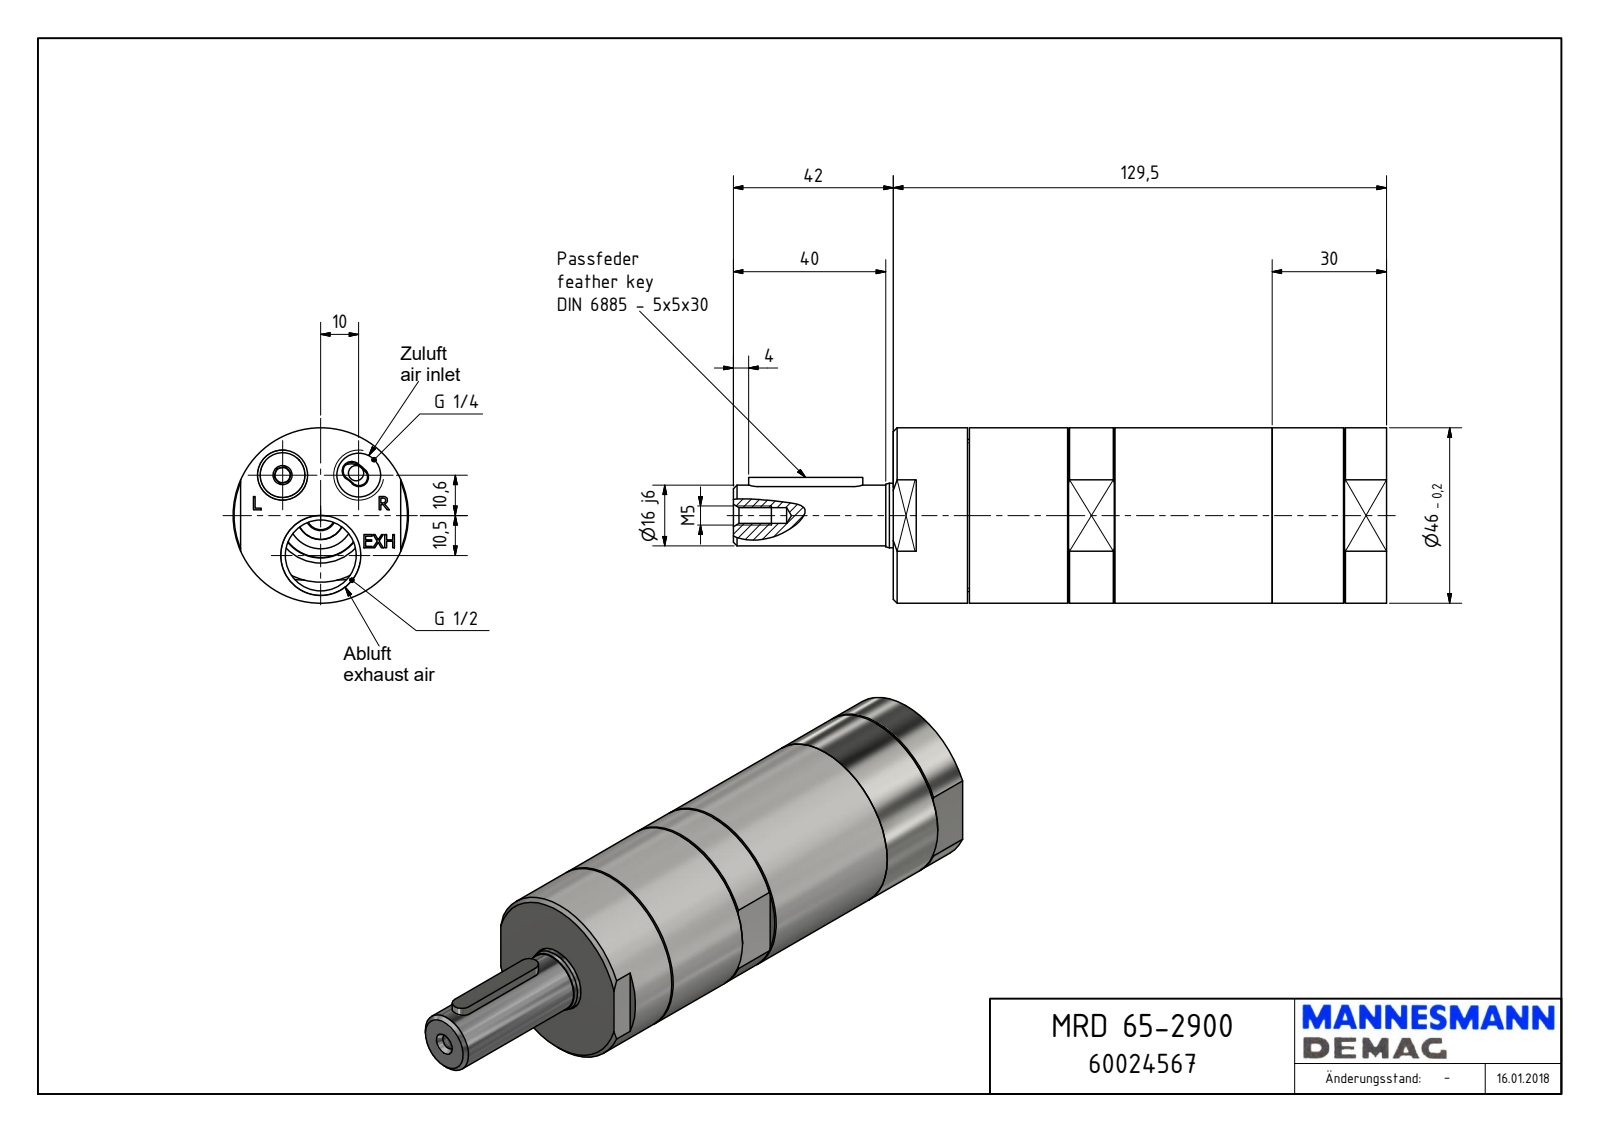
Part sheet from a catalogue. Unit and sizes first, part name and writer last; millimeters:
Units: millimetres
Overall size (bounding box): 171.5 × 46 × 46
Round holes (diameter × count): ⌀4 ×1, ⌀4.13 ×1, ⌀11.45 ×1, ⌀17.5 ×1, ⌀18.63 ×1
Round bosses / shafts (diameter × count): ⌀46 ×1, ⌀40 ×1, ⌀33.86 ×1, ⌀16.95 ×1, ⌀16 ×1
Partial cylindrical surfaces — rounded edges, fillets, slot ends (radius × count): R2.5 ×2, R5 ×2, R5.72 ×1, R19 ×1, R21.04 ×1
Main face-to-face distances: 129.5, 42, 20, 109.5, 19.5, 0.5, 110, 121.86, 102.36, 101.86
Hole centre spacings: 14.57, 23.35, 10.5, 20
Volume: 218 259 mm³ · Surface area: 27 145 mm²
Bodies: 1 solid, 163 faces (107 planar, 28 cylindrical, 28 other)
Part name (STEP PRODUCT): MRD 65-2900_60024567
STEP written by: Autodesk Inventor 2018 (AUTOMOTIVE_DESIGN)
